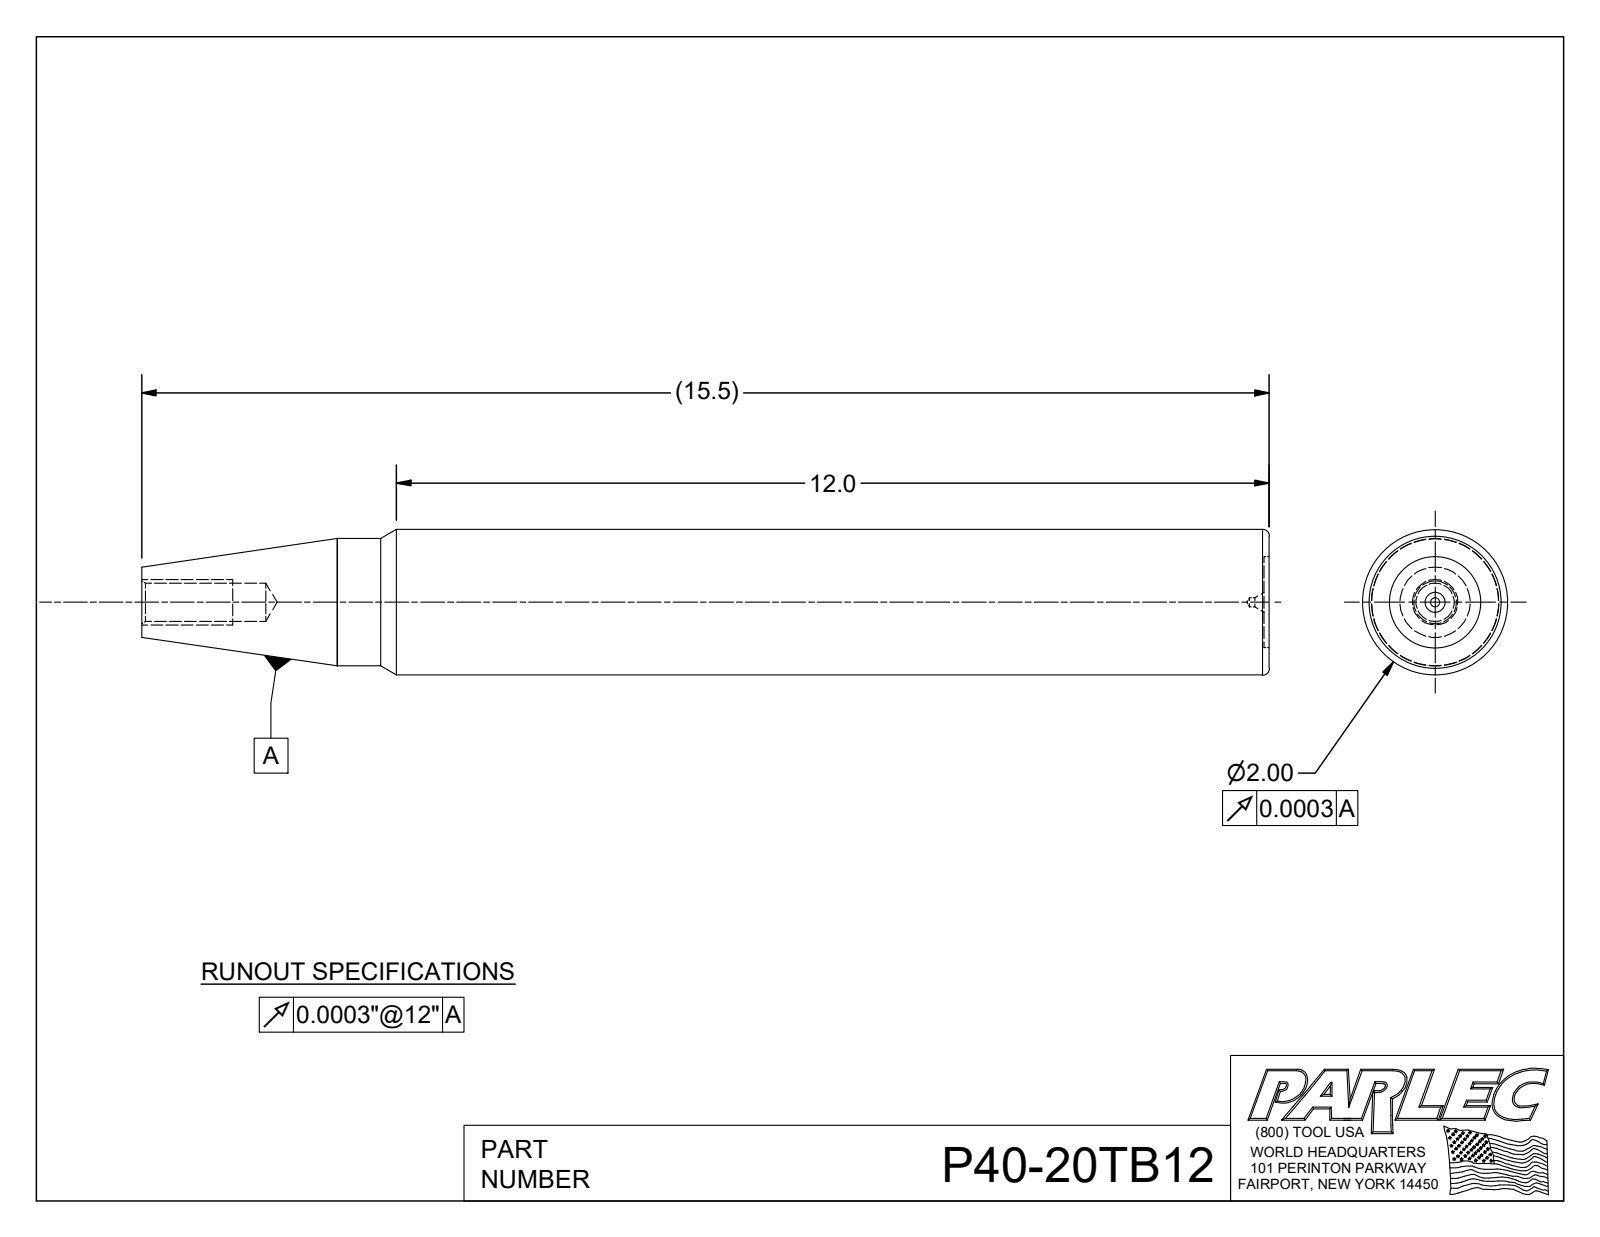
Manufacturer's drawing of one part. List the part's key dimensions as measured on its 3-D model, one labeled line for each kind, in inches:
Part name (STEP PRODUCT): P40-20TB12
STEP written by: Autodesk Inventor 2022 (AUTOMOTIVE_DESIGN)
Units: inches
Bodies: 1 solid, 25 faces (7 planar, 8 cylindrical, 10 other)
Overall size (bounding box): 15.55 × 2.75 × 2.75
Volume: 50.2 in³ · Surface area: 116.2 in²
Round holes (diameter × count): ⌀0.865 ×1
Round bosses / shafts (diameter × count): ⌀2.75 ×1, ⌀2.25 ×1, ⌀2 ×1, ⌀1.94 ×1, ⌀1.547 ×1, ⌀1.398 ×1, ⌀1.319 ×1
Main face-to-face distances: 15.55, 3.67, 11.88, 0.377, 3.293, 15.172, 0.277, 0.1, 3.393, 15.272
